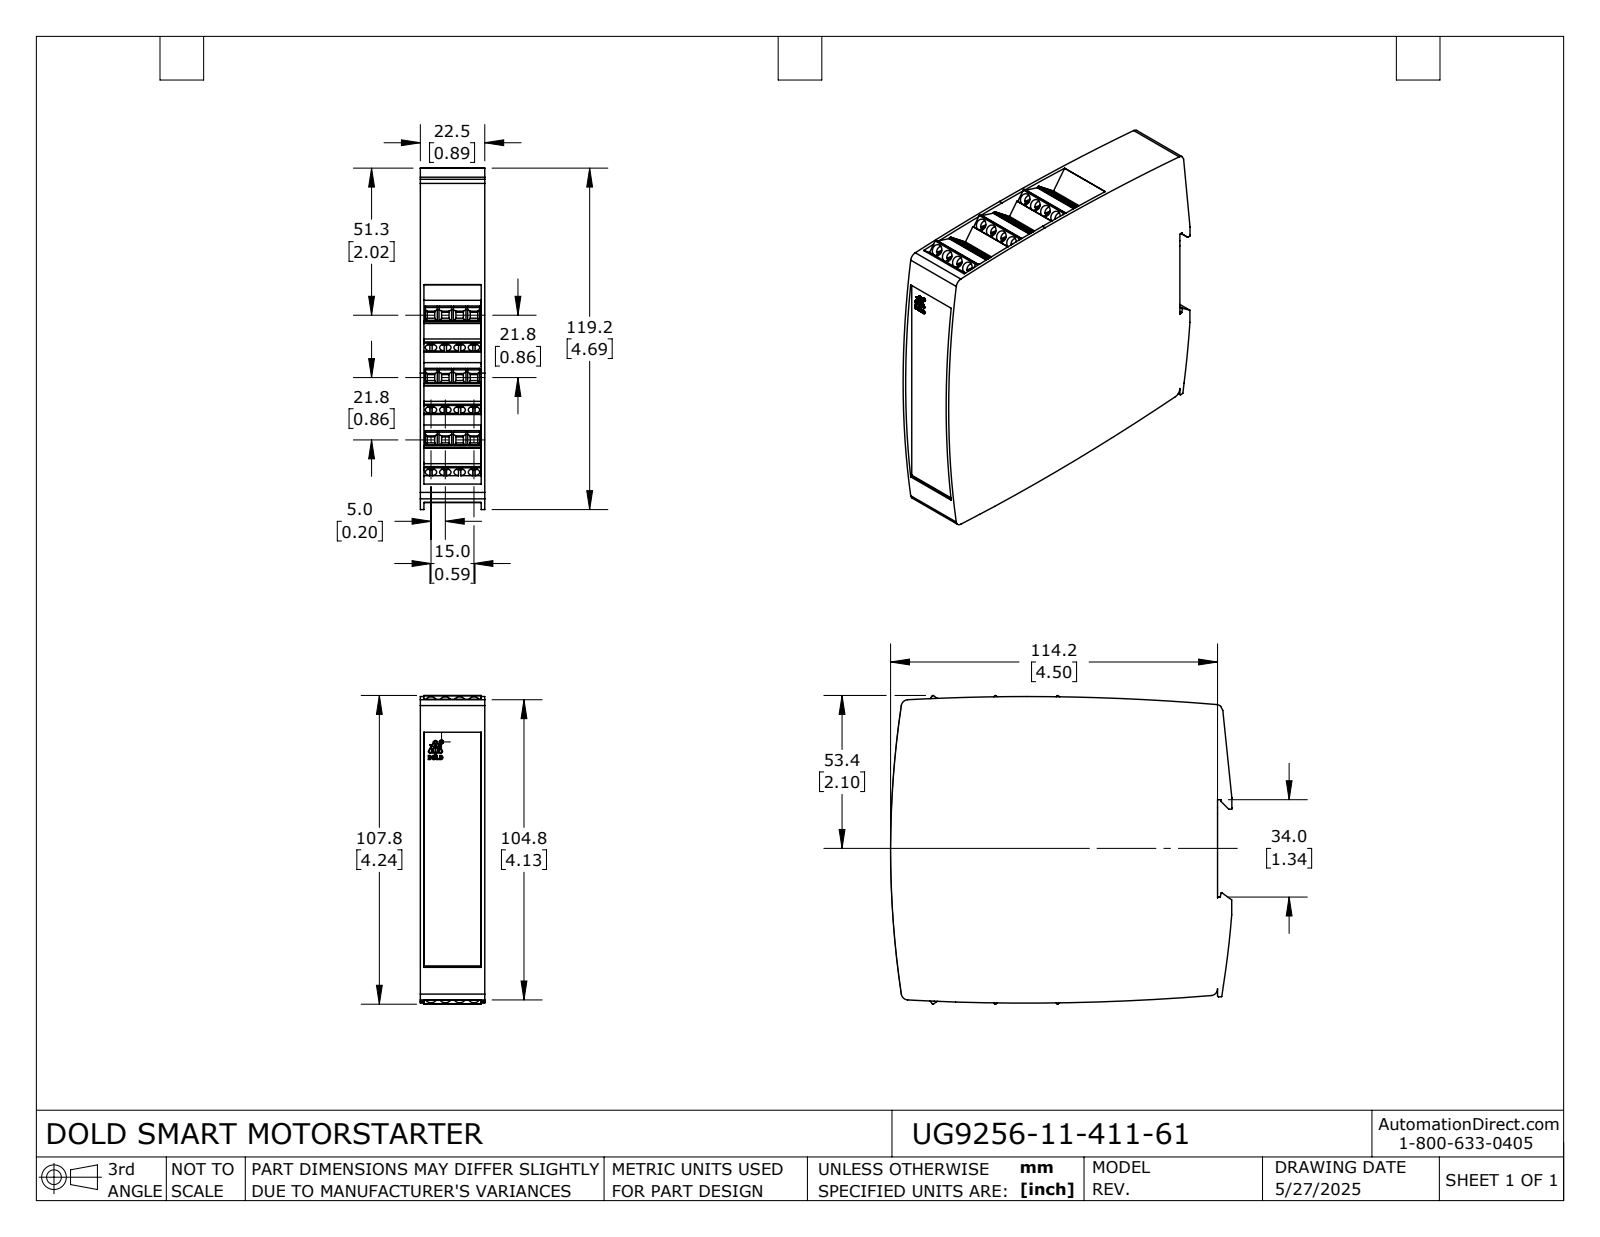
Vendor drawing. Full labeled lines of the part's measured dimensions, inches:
Part name (STEP PRODUCT): UG9256-11-411-61
STEP written by: SolidWorks 2024 (AUTOMOTIVE_DESIGN)
Units: inches
Bodies: 1 solid, 1036 faces (813 planar, 222 cylindrical, 1 other)
Overall size (bounding box): 4.693 × 4.243 × 0.886
Volume: 15.85 in³ · Surface area: 64.72 in²
Round holes (diameter × count): ⌀0.157 ×24, ⌀0.053 ×1
Round bosses / shafts (diameter × count): ⌀0.15 ×24, ⌀0.049 ×1
Partial cylindrical surfaces — rounded edges, fillets, slot ends (radius × count): R0.012 ×15, R0.02 ×14, R0.004 ×12, R0.094 ×7, R0.005 ×6, R0.004 ×4, R31.496 ×4, R0.021 ×3
Main face-to-face distances: 0.886, 0.049, 0.837, 0.675, 4.379, 0.051, 0.835, 1.35, 0.528, 0.785
Hole centre spacings: 0.563, 0.197, 0.528, 0.658, 0.394, 1.073, 0.792, 1.055
